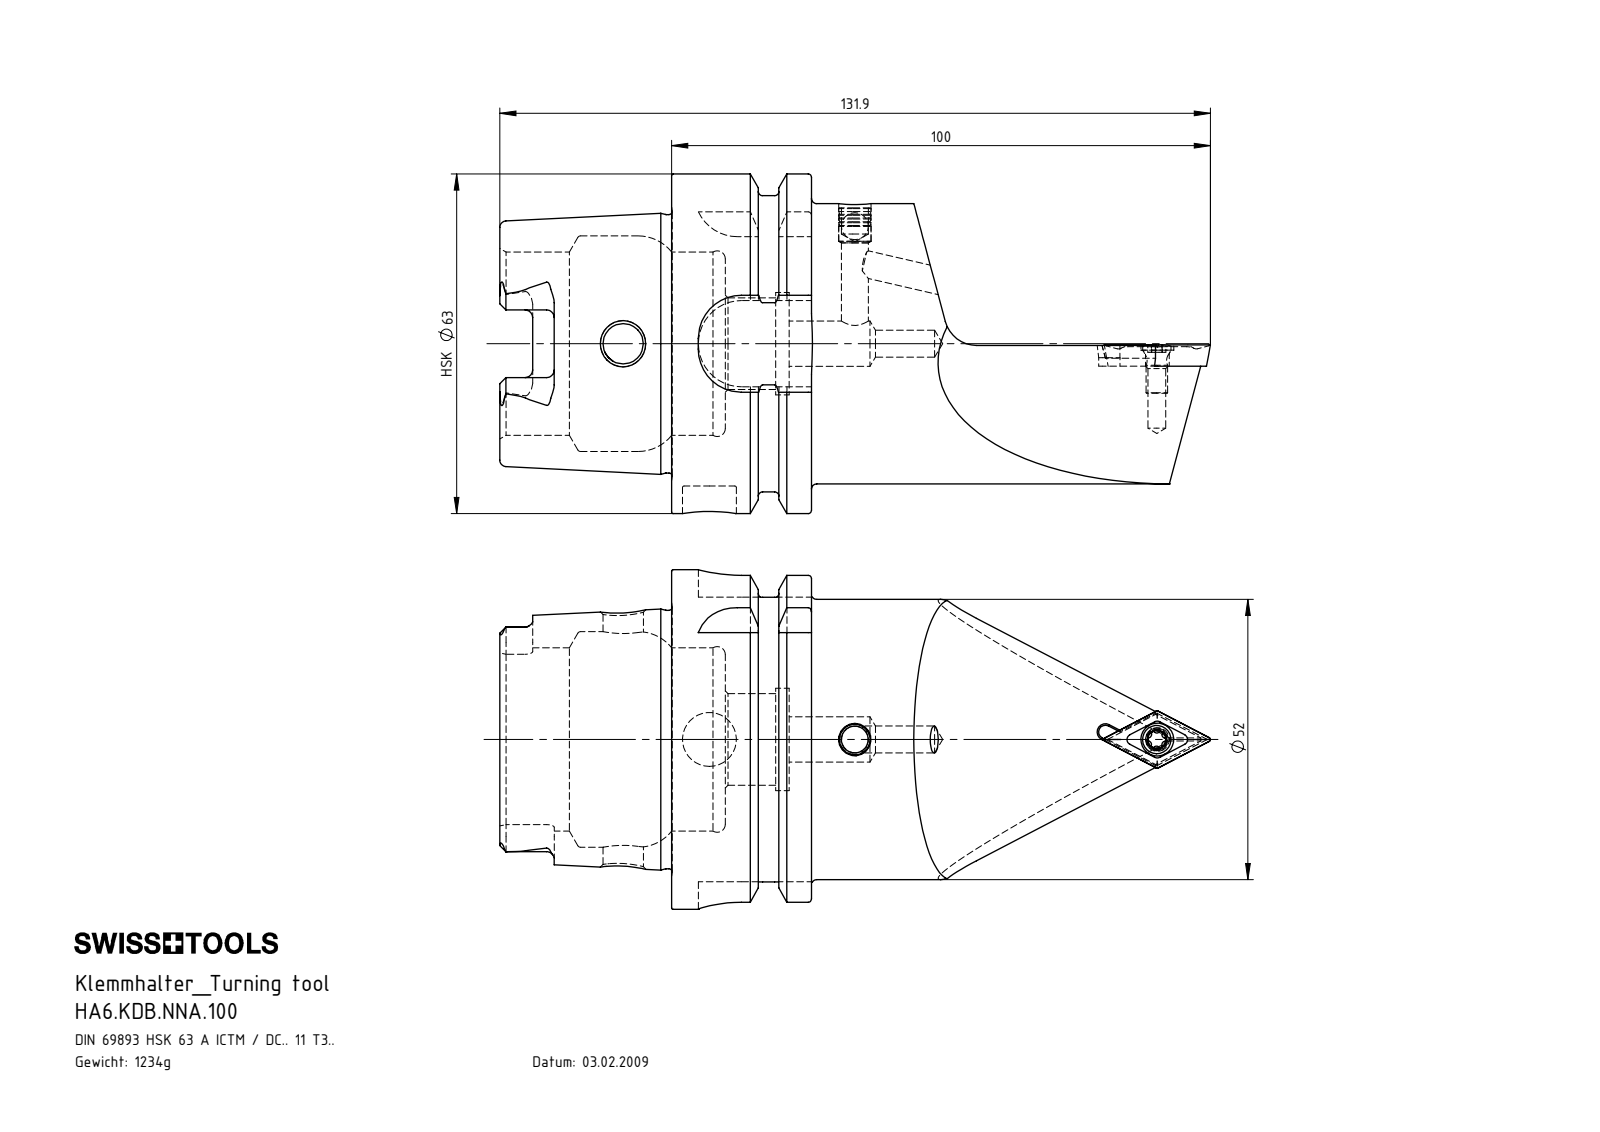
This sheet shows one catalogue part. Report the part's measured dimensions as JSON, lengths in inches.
{"part_name": "HA6.KDB.NNA.100; KVT_MB_600_060; HA6-KDB.NNA.100_C; DCMT11T304 (+1 more)", "step_written_by": "SolidWorks 2017 (AUTOMOTIVE_DESIGN)", "units": "inches", "bodies": {"solids": 5, "faces": 234, "planar": 80, "cylindrical": 57, "other": 97}, "overall_size": [5.193, 2.48, 2.48], "volume_in3": 9.583, "surface_area_in2": 48.74, "round_holes": [[0.197, 3], [0.13, 1], [0.173, 1], [0.24, 1], [0.295, 1], [0.331, 1], [0.394, 1], [0.669, 1], [0.748, 1], [1.339, 1], [1.575, 1]], "round_bosses_or_shafts": [[2.48, 1], [2.163, 1], [2.047, 1], [1.887, 1], [0.236, 1], [0.207, 1], [0.157, 1]], "partial_cylinders_radius": [[0.013, 6], [0.023, 6], [0.055, 6], [0.315, 4], [0.111, 2], [0.113, 2], [0.049, 1], [0.236, 1]], "face_to_face_distances": [1.022, 0.63, 0.392, 1.256, 1.648, 2.278, 2.079, 0.858, 0.467, 2.114], "hole_center_spacings": [1.063, 2.207, 2.211, 3.27, 3.274]}
